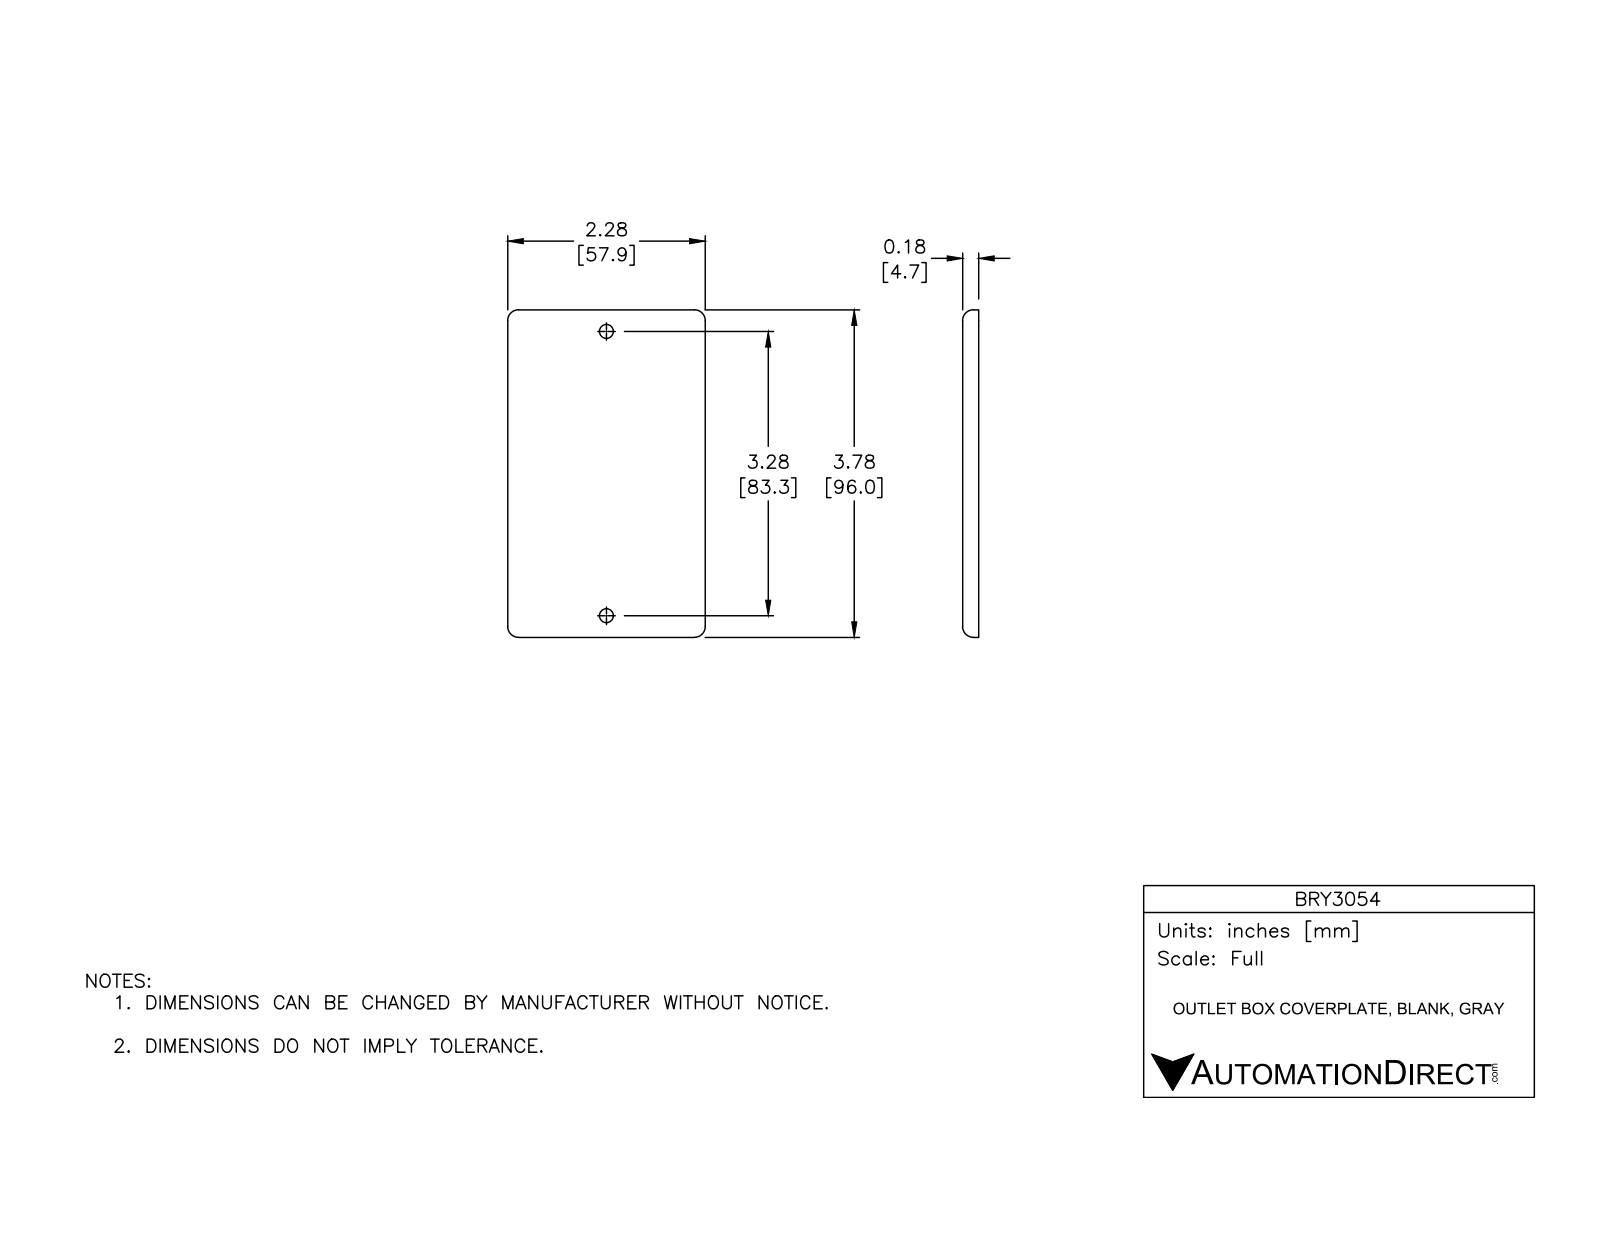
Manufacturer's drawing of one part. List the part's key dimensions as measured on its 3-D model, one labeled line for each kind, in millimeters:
Part name (STEP PRODUCT): BRY3054
STEP written by: SolidWorks 2016 (AUTOMOTIVE_DESIGN)
Units: millimetres
Bodies: 1 solid, 55 faces (23 planar, 28 cylindrical, 4 other)
Overall size (bounding box): 96.5 × 58.2 × 4.7
Volume: 21 200 mm³ · Surface area: 12 930 mm²
Round holes (diameter × count): ⌀4.1 ×2
Round bosses / shafts (diameter × count): ⌀7.7 ×2
Partial cylindrical surfaces — rounded edges, fillets, slot ends (radius × count): R3.2 ×12, R1.4 ×4, R1.7 ×4
Main face-to-face distances: 3.7, 3.9, 0.8, 1, 4.7, 1.5, 1.8, 10, 48.1, 58.2
Hole centre spacings: 83.3
